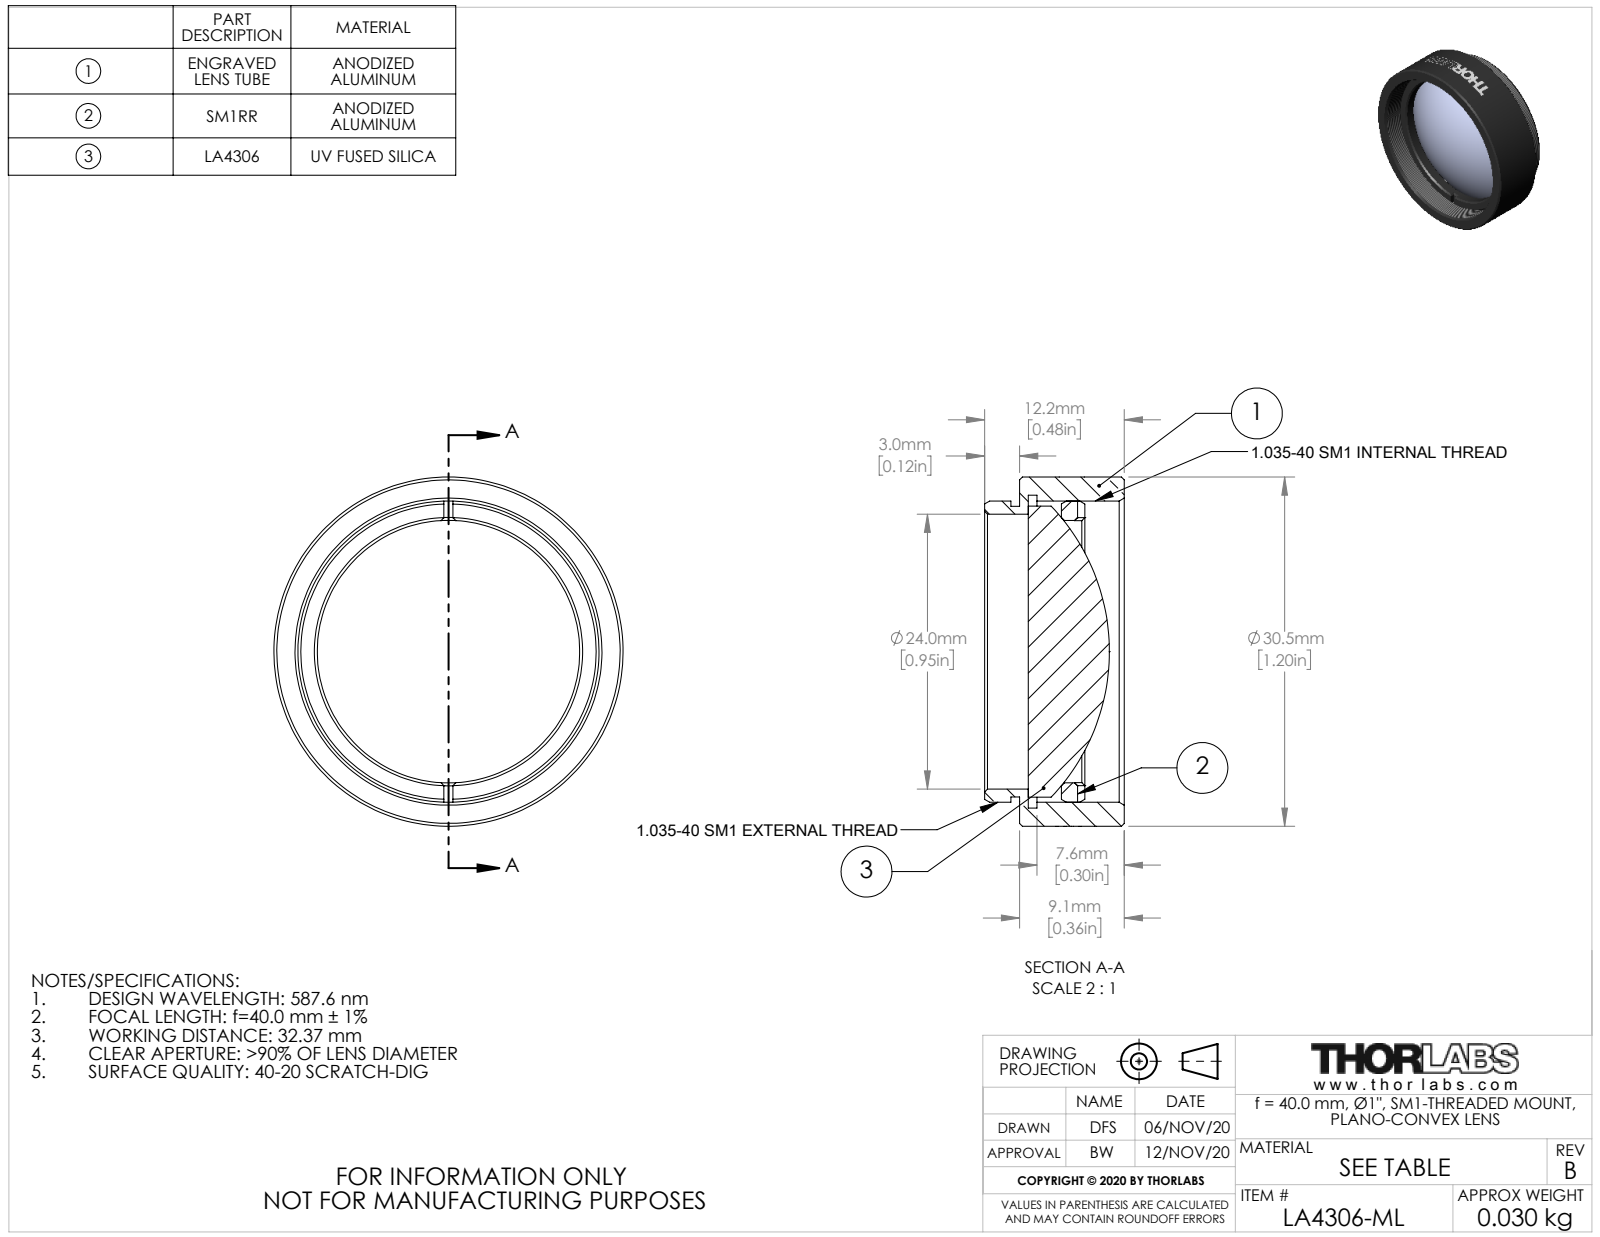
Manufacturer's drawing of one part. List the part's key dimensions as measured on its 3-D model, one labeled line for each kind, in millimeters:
Part name (STEP PRODUCT): 24458-E0W
STEP written by: SolidWorks 2018 (CONFIG_CONTROL_DESIGN)
Units: millimetres
Bodies: 3 solids, 122 faces (20 planar, 78 cylindrical, 24 other)
Overall size (bounding box): 30.48 × 30.48 × 12.19
Volume: 4 593 mm³ · Surface area: 4 529 mm²
Round holes (diameter × count): ⌀22.91 ×1, ⌀24 ×1, ⌀27.3 ×1
Round bosses / shafts (diameter × count): ⌀30.48 ×1, ⌀26.29 ×1, ⌀25.4 ×1, ⌀25.37 ×1
Main face-to-face distances: 0.77, 9.15, 8.38, 3.67, 2.9, 5.48, 5.7, 4.93, 2.03, 3.45
